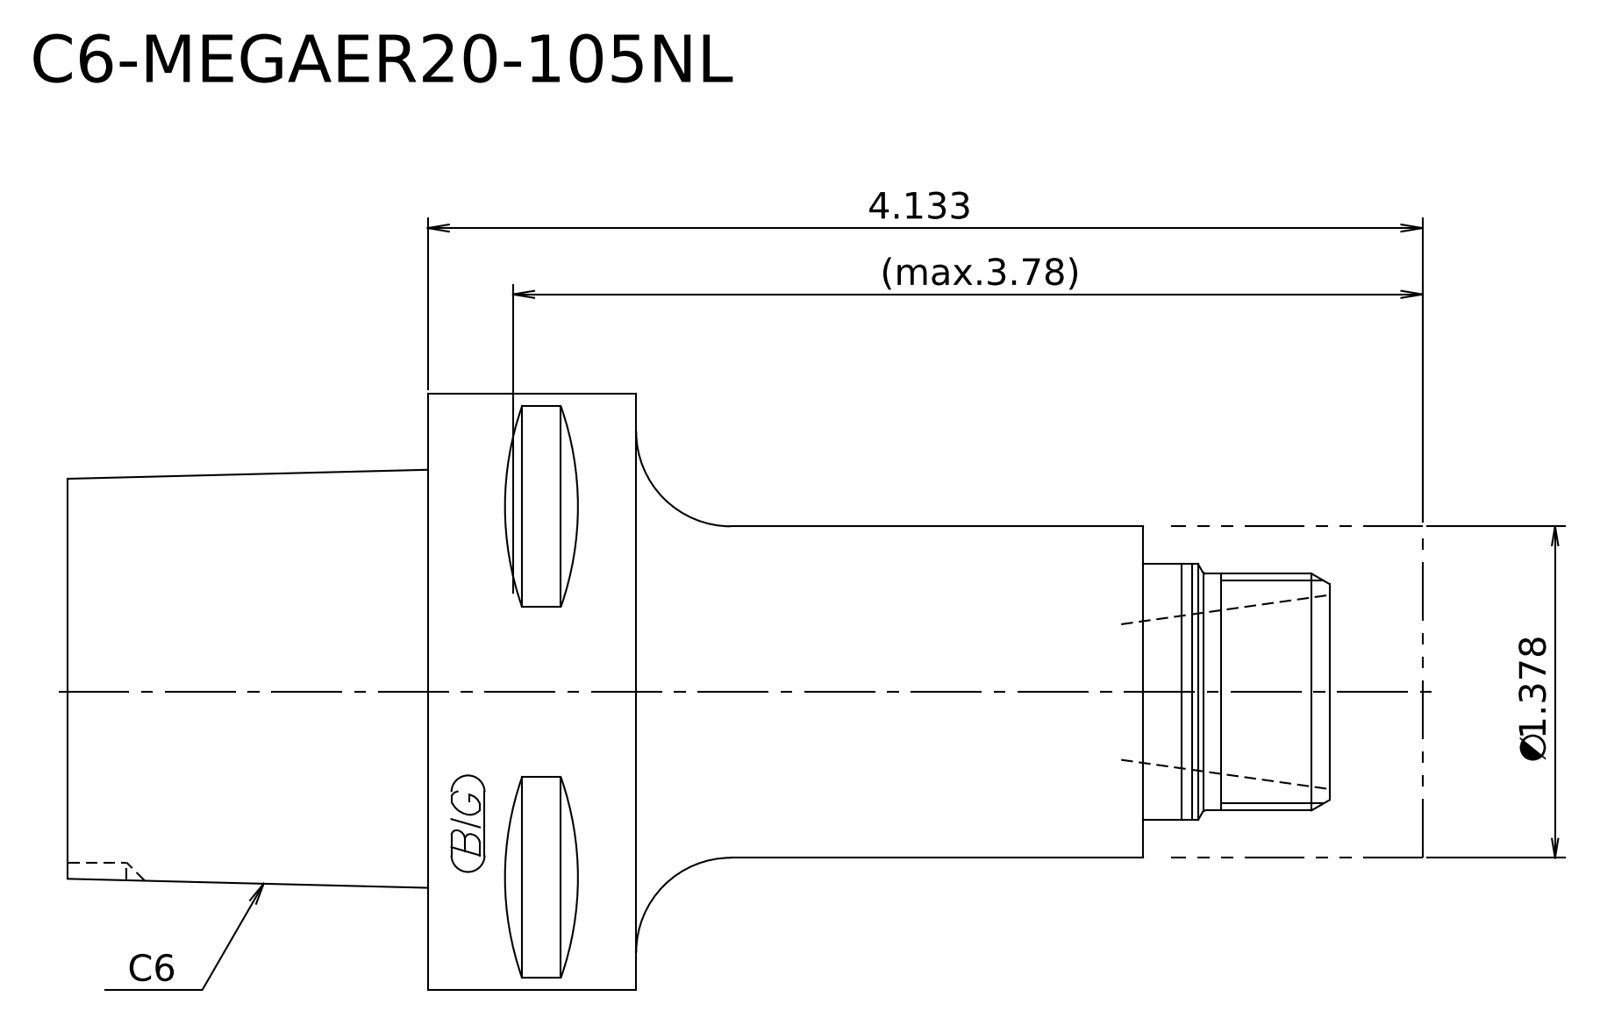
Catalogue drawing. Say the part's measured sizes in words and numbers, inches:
Its 3-D file was written by "Kubotek KeyCreator 2011 V10.0.2 (22737) (automotive_design)". It is 2 solids with 18 faces: 7 planar, 5 cylindrical and 6 other. Overall it measures 5.63 by 2.48 by 2.48 inches. Its volume is 13.24 cubic inches and its surface area 42.33 square inches. Round bosses or shafts: 1 of diameter 2.48, 1 of diameter 1.378, 1 of diameter 1.063, 1 of diameter 0.984. The main face-to-face distances are 1.496, 3.091, 4.587, 1.043, 4.134, 5.63, 3.268, 2.224, 0.866, 2.362.
